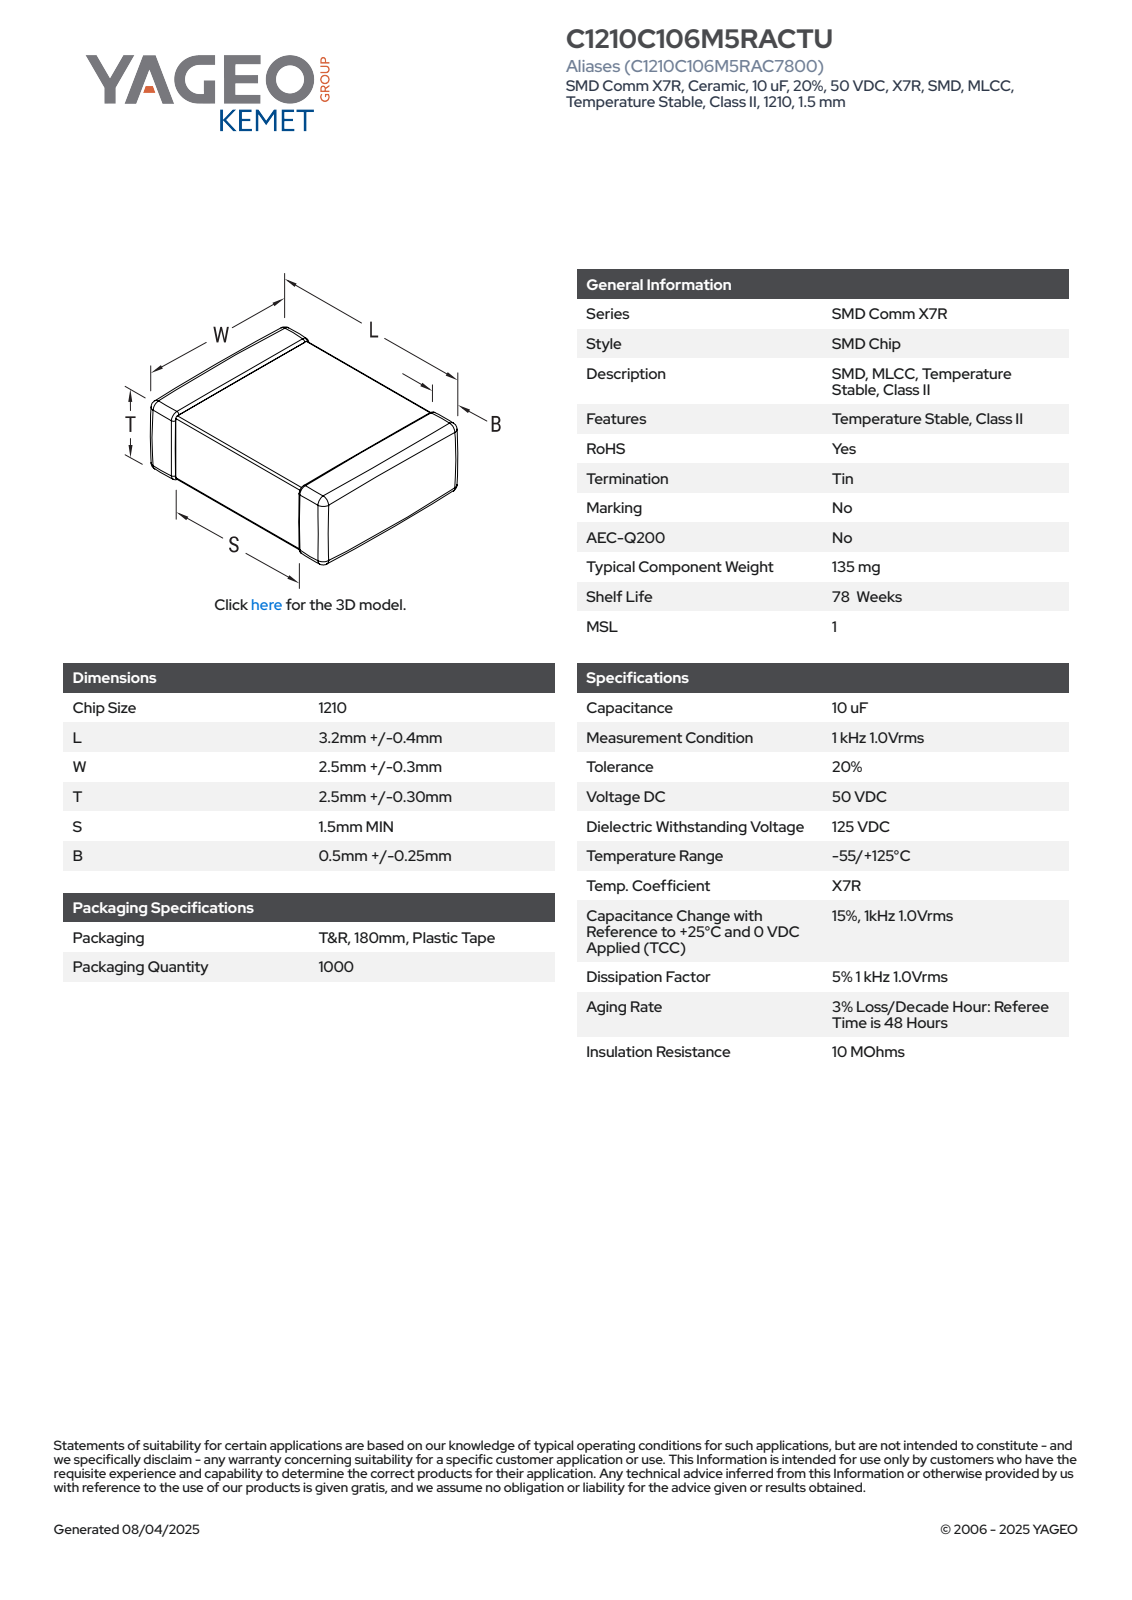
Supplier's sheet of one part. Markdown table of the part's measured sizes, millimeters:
| quantity | value |
| --- | --- |
| part name | CCS_CCSTD_1210_L3.6W2.8T2.8B0.5 |
| STEP written by | SolidWorks 2021 (AUTOMOTIVE_DESIGN) |
| units | millimeters |
| bodies | 4 solids, 125 faces (71 planar, 38 cylindrical, 16 other) |
| overall size | 3.6 × 2.8 × 2.8 |
| volume | 27 mm³ |
| surface area | 56 mm² |
| main face-to-face distances | 2.74, 2.68, 3.6, 2.8, 2.75, 2.69, 1.53, 2.07, 1.94, 0.41 |
